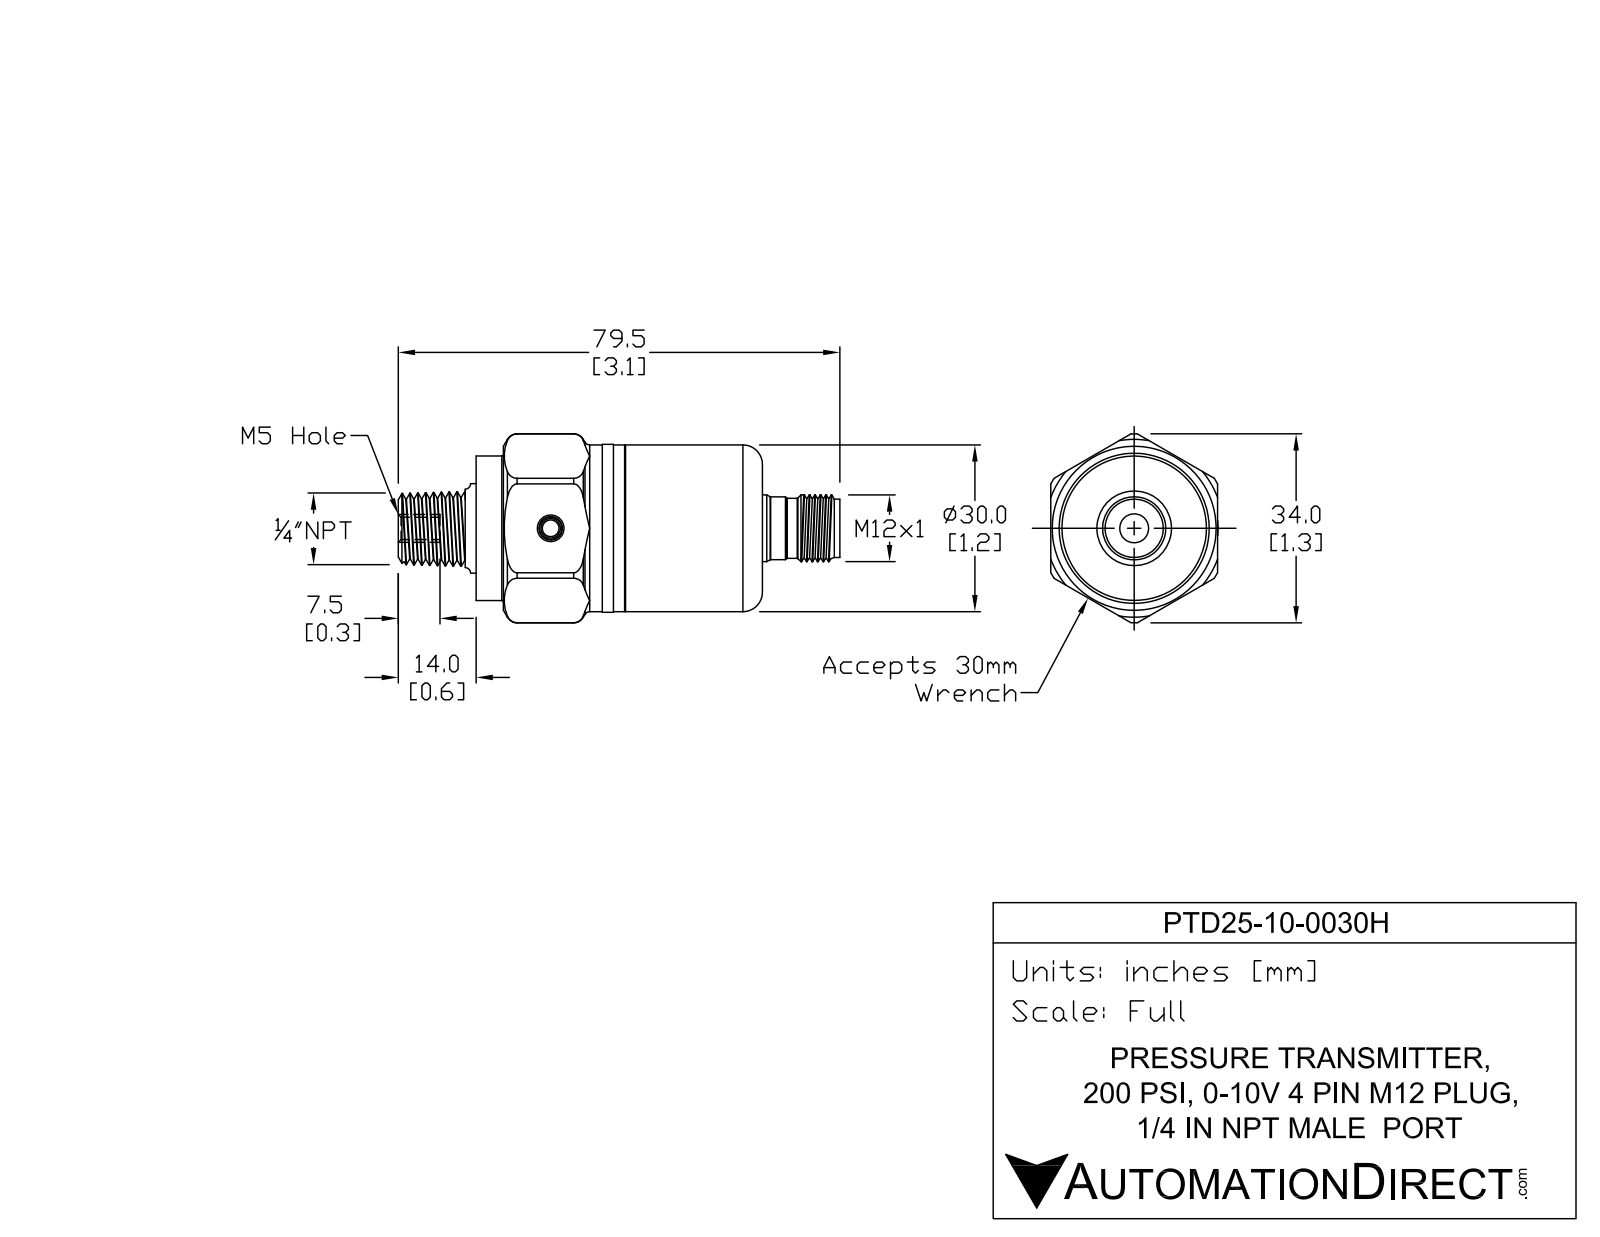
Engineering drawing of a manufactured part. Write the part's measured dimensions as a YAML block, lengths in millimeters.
part_name: "PTD25-10-0200H"
step_written_by: "SolidWorks 2017 (AUTOMOTIVE_DESIGN)"
units: millimeters
bodies: {solids: 1, faces: 124, planar: 36, cylindrical: 59, other: 29}
overall_size: [79.5, 33.78, 31.7]
volume: 39212
surface_area: 8088
round_holes:
  - {diameter: 4, count: 1}
  - {diameter: 8.5, count: 1}
round_bosses_or_shafts:
  - {diameter: 30.05, count: 1}
  - {diameter: 30, count: 1}
  - {diameter: 25.96, count: 1}
  - {diameter: 14, count: 1}
  - {diameter: 13.5, count: 1}
  - {diameter: 12, count: 1}
partial_cylinders:
  - {radius: 3.76, count: 1}
  - {radius: 16.95, count: 1}
face_to_face_distances: [51, 29.98, 30, 48, 3, 65, 17, 14, 30.01, 5.65]
